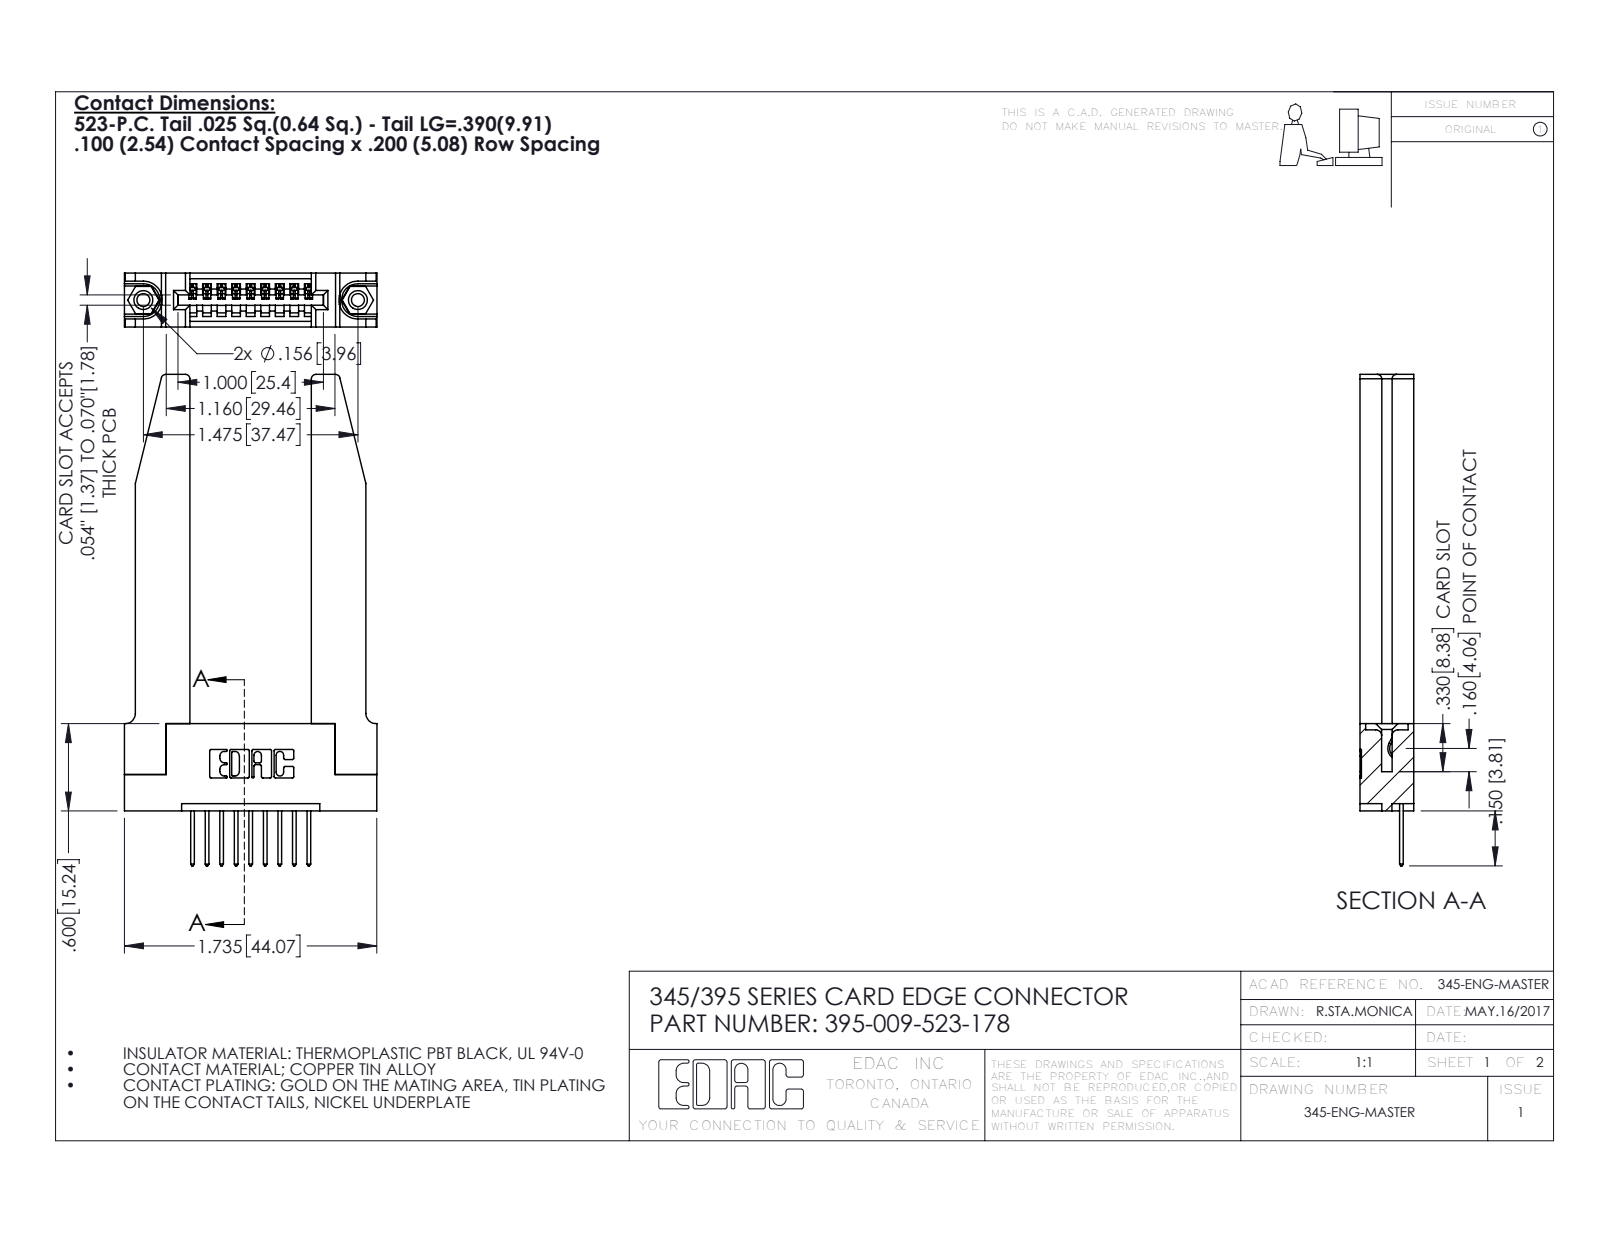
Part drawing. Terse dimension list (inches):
name: 345-292-001_345-293-123; 395-009-523-178; 345-250-001_345-250-001-102; 345-220-078_345-220-078 (+1 more)
written by: SolidWorks 2016 (CONFIG_CONTROL_DESIGN)
unit: in
bodies: 14 solids, 882 faces (582 planar, 248 cylindrical, 52 other)
size: 3.377 × 1.736 × 0.37
volume: 0.713 in³; area: 17.99 in²
holes: 2× ⌀0.089, 2× ⌀0.125, 2× ⌀0.156, 1× ⌀0.064
bosses: 2× ⌀0.155
rounds: 22× R0.01, 18× R0.006, 18× R0.01, 8× R0.03, 6× R0.007, 6× R0.031, 3× R0.026, 2× R0.031
face distances: 0.37, 0.072, 0.298, 0.15, 0.148, 0.22, 0.2, 0.077, 0.835, 0.098
hole spacings: 0.27, 1.244, 1.475
